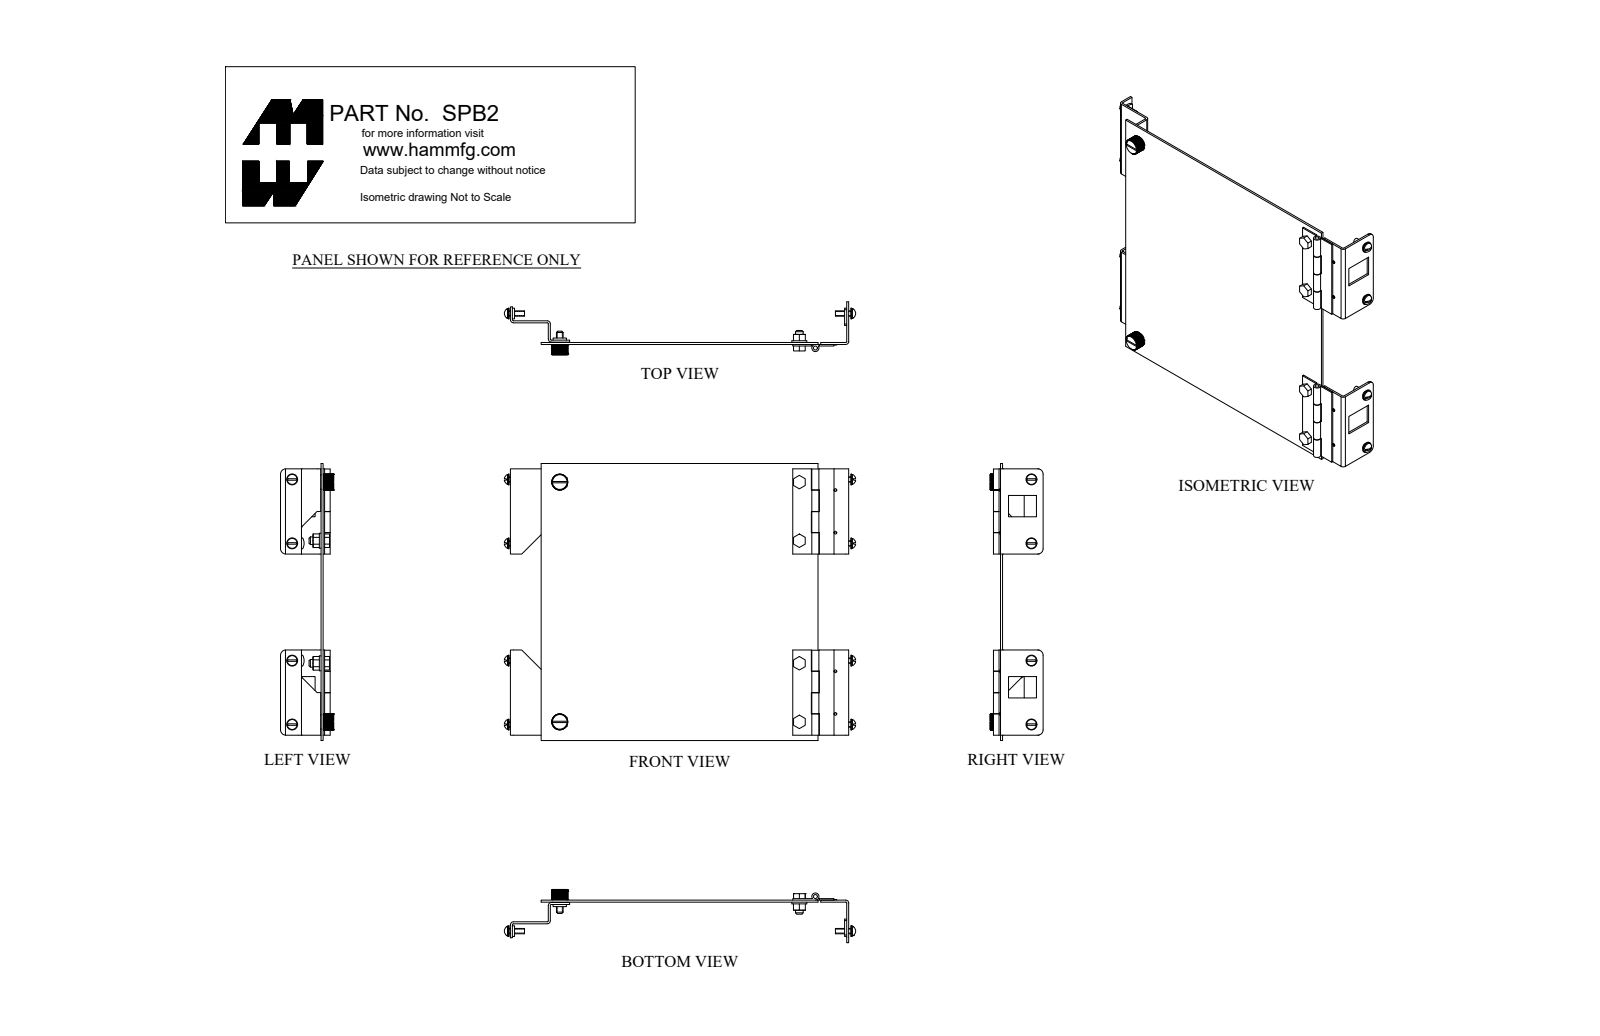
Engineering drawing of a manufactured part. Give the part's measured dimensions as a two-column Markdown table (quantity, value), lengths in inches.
| quantity | value |
| --- | --- |
| part name | SPB2 |
| STEP written by | SolidWorks 2018 (AUTOMOTIVE_DESIGN) |
| units | inches |
| bodies | 47 solids, 1420 faces (872 planar, 438 cylindrical, 110 other) |
| overall size | 16.493 × 13 × 2.5 |
| volume | 24.09 in³ |
| surface area | 528.6 in² |
| round holes (diameter × count) | 0.313 × 12, 0.201 × 8, 0.26 × 8, 0.375 × 6, 0.5 × 4, 0.257 × 2, 0.187 × 1 |
| round bosses / shafts (diameter × count) | 0.25 × 10, 0.51 × 8, 0.465 × 8, 0.293 × 8, 0.7 × 4, 0.36 × 4, 0.131 × 4, 0.625 × 2 |
| partial cylindrical surfaces (radius × count) | 0.5 × 20, 0.013 × 10, 0.028 × 10, 0.13 × 10, 0.048 × 4, 0.143 × 4, 0.25 × 4, 0.375 × 2 |
| main face-to-face distances | 0.095, 1.015, 0.095, 0.072, 0.167, 1.087, 0.92, 1.182, 1.11, 1.78 |
| hole center spacings | 8.5, 3, 11.25, 5.5, 11.25, 11.5, 2.75, 11.581 |
